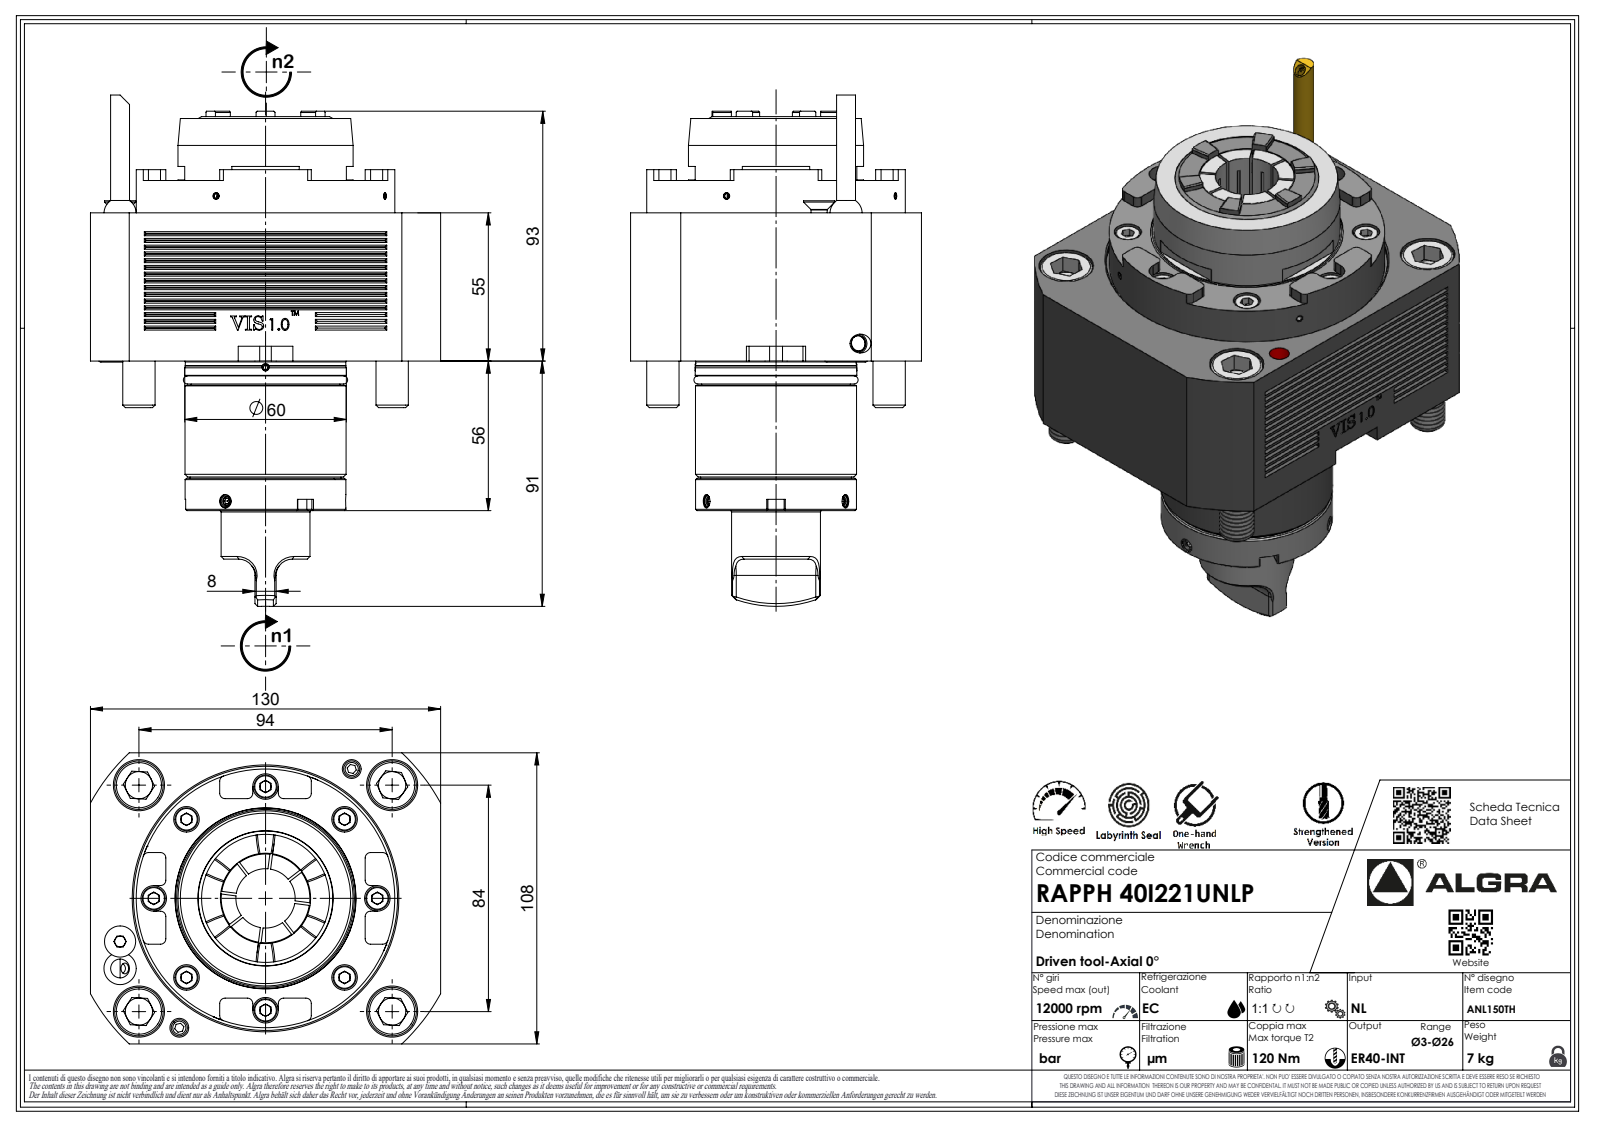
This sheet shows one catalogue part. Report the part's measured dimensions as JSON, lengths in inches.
{"part_name": "RAPPH40I221UNLP", "step_written_by": "SolidWorks 2023 (AUTOMOTIVE_DESIGN)", "units": "inches", "bodies": {"solids": 1, "faces": 554, "planar": 363, "cylindrical": 88, "other": 103}, "overall_size": [7.126, 5.118, 4.252], "volume_in3": 66.03, "surface_area_in2": 123.3, "round_holes": [[0.374, 4], [0.083, 1]], "round_bosses_or_shafts": [[0.472, 4], [3.78, 1], [2.559, 1], [2.362, 1], [2.354, 1], [2.35, 1], [2.346, 1], [2.173, 1]], "partial_cylinders_radius": [[0.079, 24], [0.315, 8], [0.013, 7], [0.02, 7], [0.146, 7], [0.236, 6], [0.118, 3], [0.008, 1]], "face_to_face_distances": [2.165, 4.252, 5.118, 1.378, 2.638, 3.543, 0.472, 0.906, 0.217, 1.949], "hole_center_spacings": [2.311, 3.268]}
